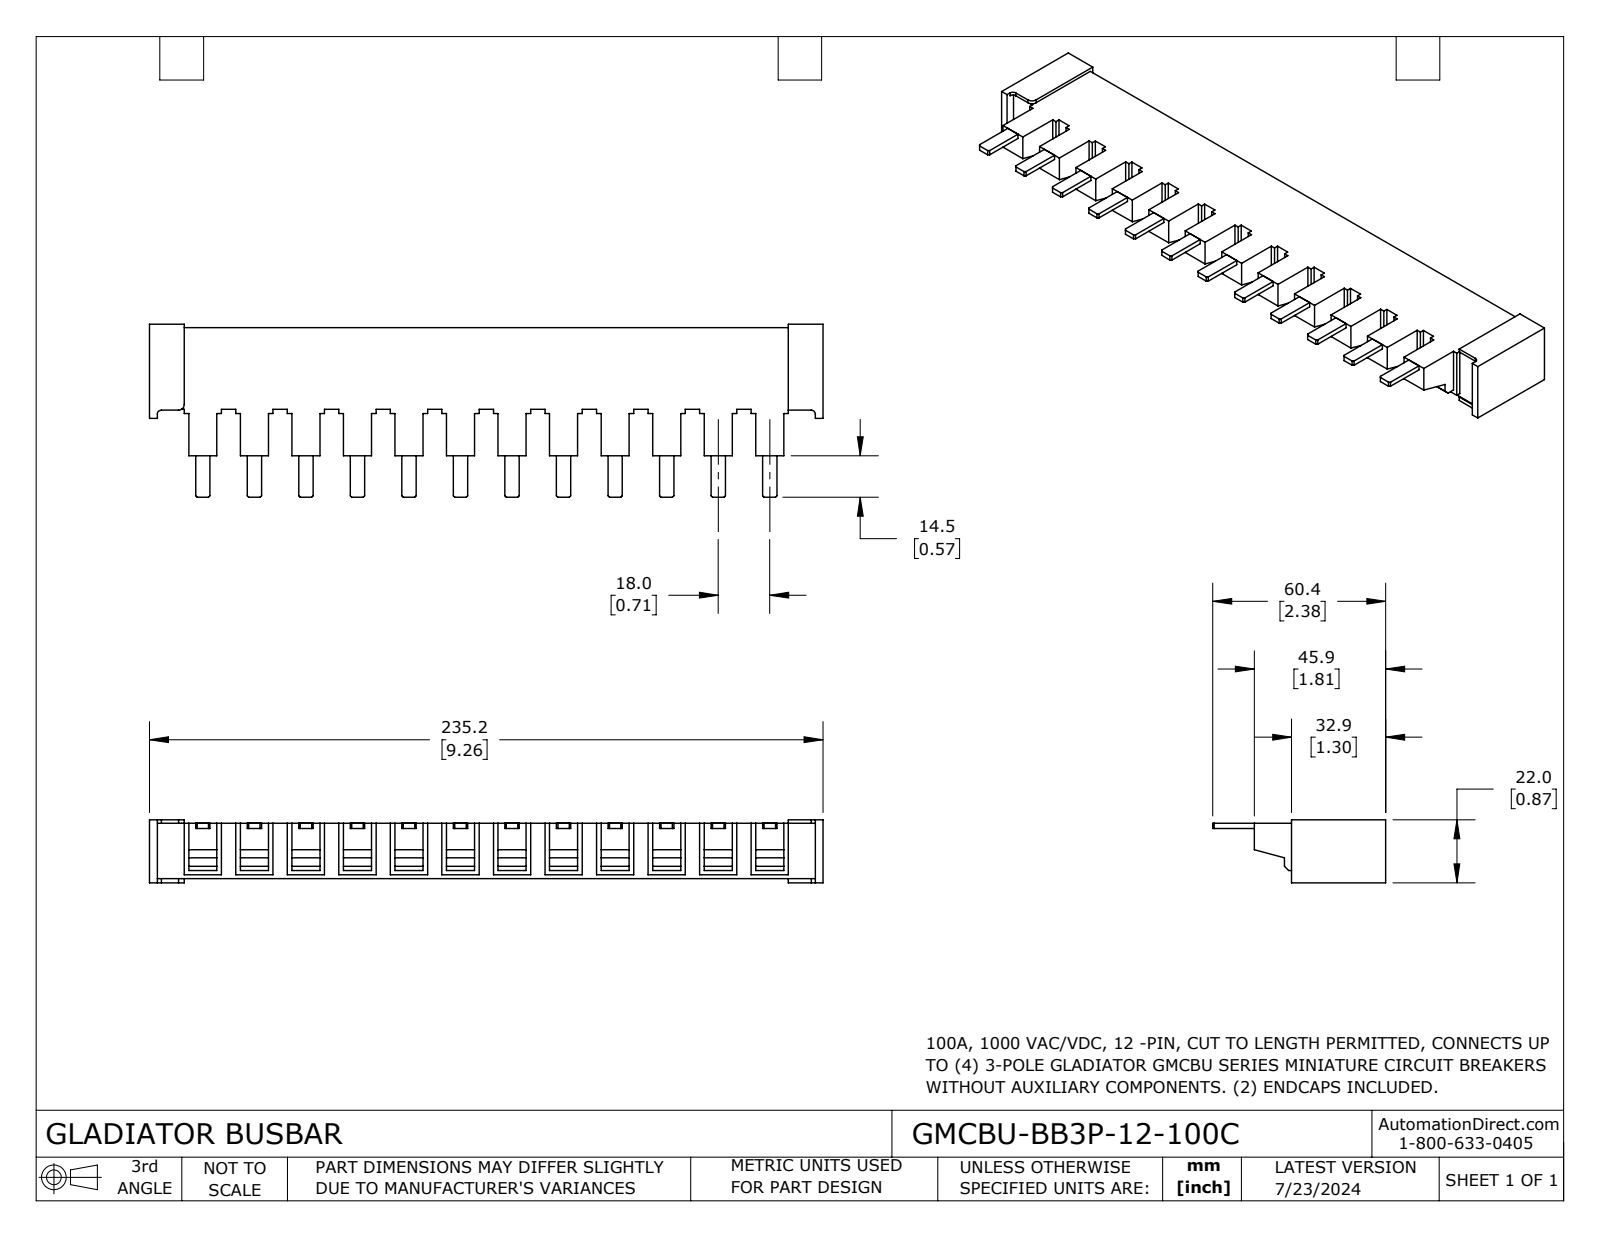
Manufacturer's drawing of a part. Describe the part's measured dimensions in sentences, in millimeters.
The part is named "GMCBU-BB3P-12-100C". Its 3-D file was written by "SolidWorks 2023 (CONFIG_CONTROL_DESIGN)". It is 1 solid with 248 faces: 242 planar, 6 cylindrical and 0 other. Overall it measures 235.2 by 60.4 by 22 millimeters. Its volume is 159 200 cubic millimeters and its surface area 35 370 square millimeters. Partial cylindrical surfaces (rounded edges, fillets, slot ends): 2 of radius 1.4, 1 of radius 2. The main face-to-face distances are 19.3, 18, 36, 54, 1.5, 72, 28.5, 90, 1.2, 108.
